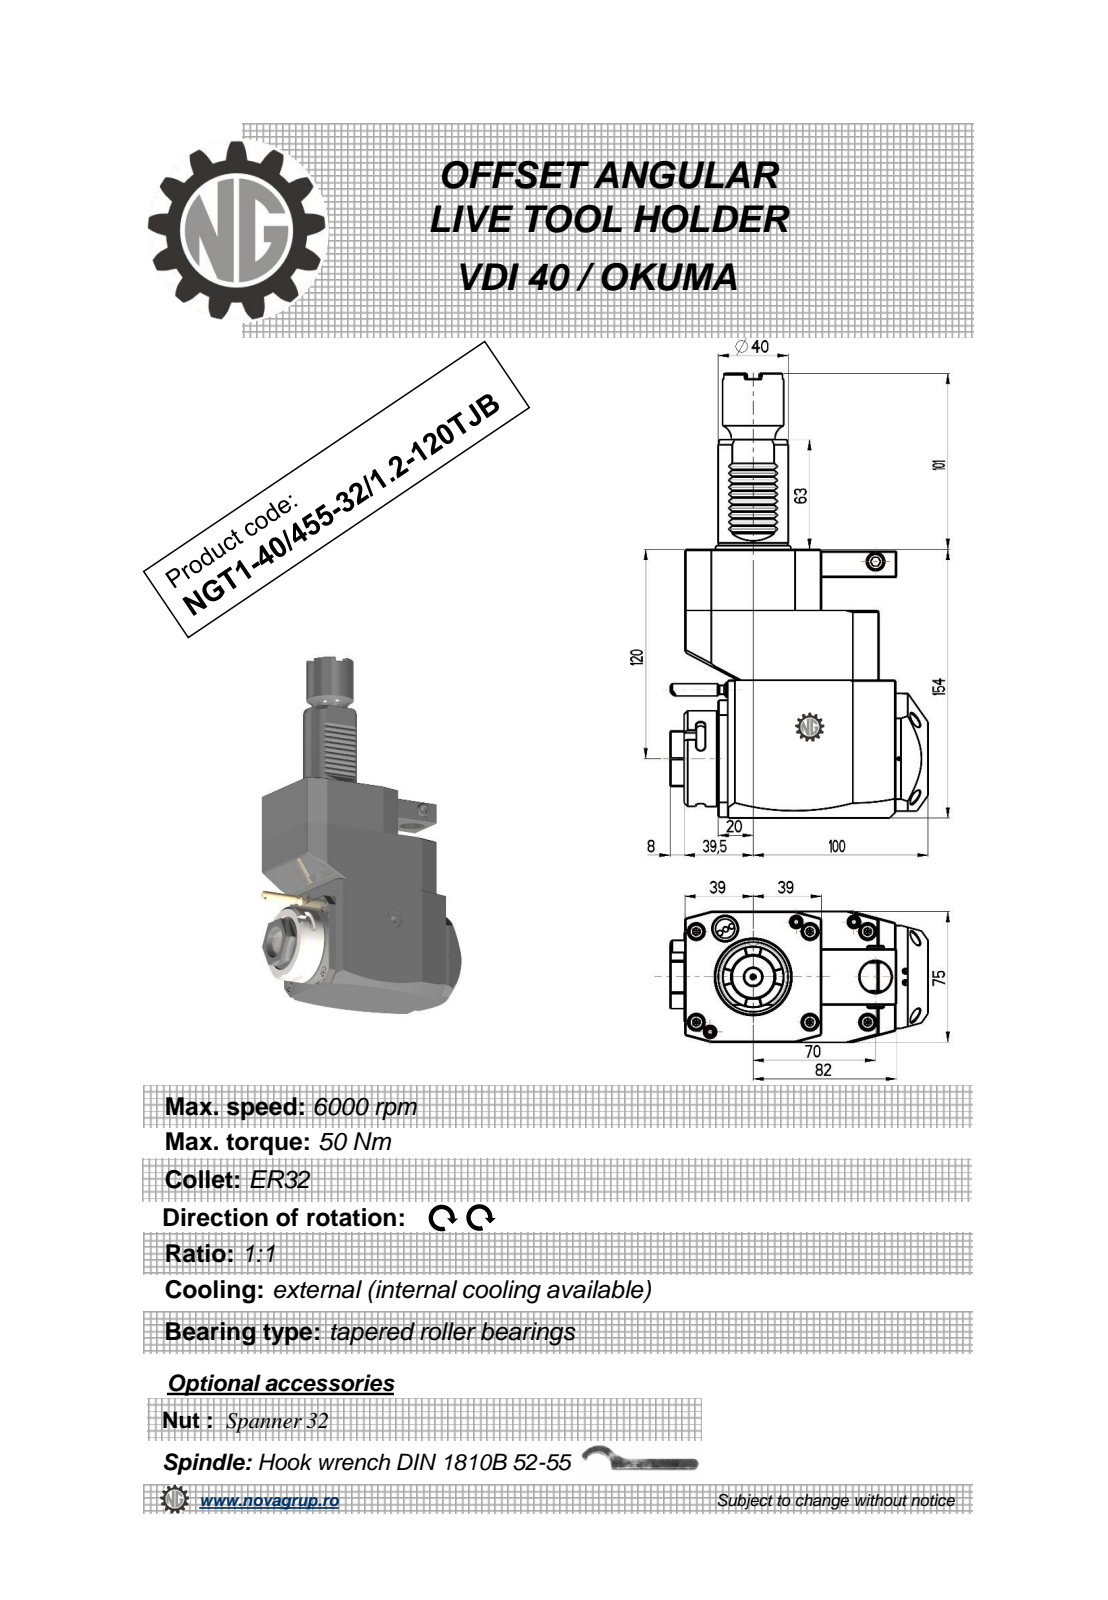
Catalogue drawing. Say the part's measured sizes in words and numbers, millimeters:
The part is named "NGT1_40_455_32_1_2_120TJB". Its 3-D file was written by "PRO/ENGINEER BY PARAMETRIC TECHNOLOGY CORPORATION, 2010280 (CONFIG_CONTROL_DESIGN)". It is 1 solid with 375 faces: 205 planar, 64 cylindrical and 106 other. Overall it measures 255 by 147.5 by 75 millimeters. Its volume is 1 311 000 cubic millimeters and its surface area 95 400 square millimeters. Round holes: 1 of diameter 2.5, 1 of diameter 3, 1 of diameter 9.5, 1 of diameter 18, 1 of diameter 23, 1 of diameter 25. Round bosses or shafts: 2 of diameter 8.96, 1 of diameter 55, 1 of diameter 48, 1 of diameter 40, 1 of diameter 35, 1 of diameter 10, 1 of diameter 7, 1 of diameter 5. Partial cylindrical surfaces (rounded edges, fillets, slot ends): 10 of radius 0.3, 6 of radius 2.5, 2 of radius 180, 1 of radius 0.5, 1 of radius 4.25, 1 of radius 24.5, 1 of radius 37.5. The main face-to-face distances are 75, 154, 19, 59, 0.5, 111, 92, 35, 119, 53.5. The hole center spacings are 43.2, 70, 75.07, 112.5.
